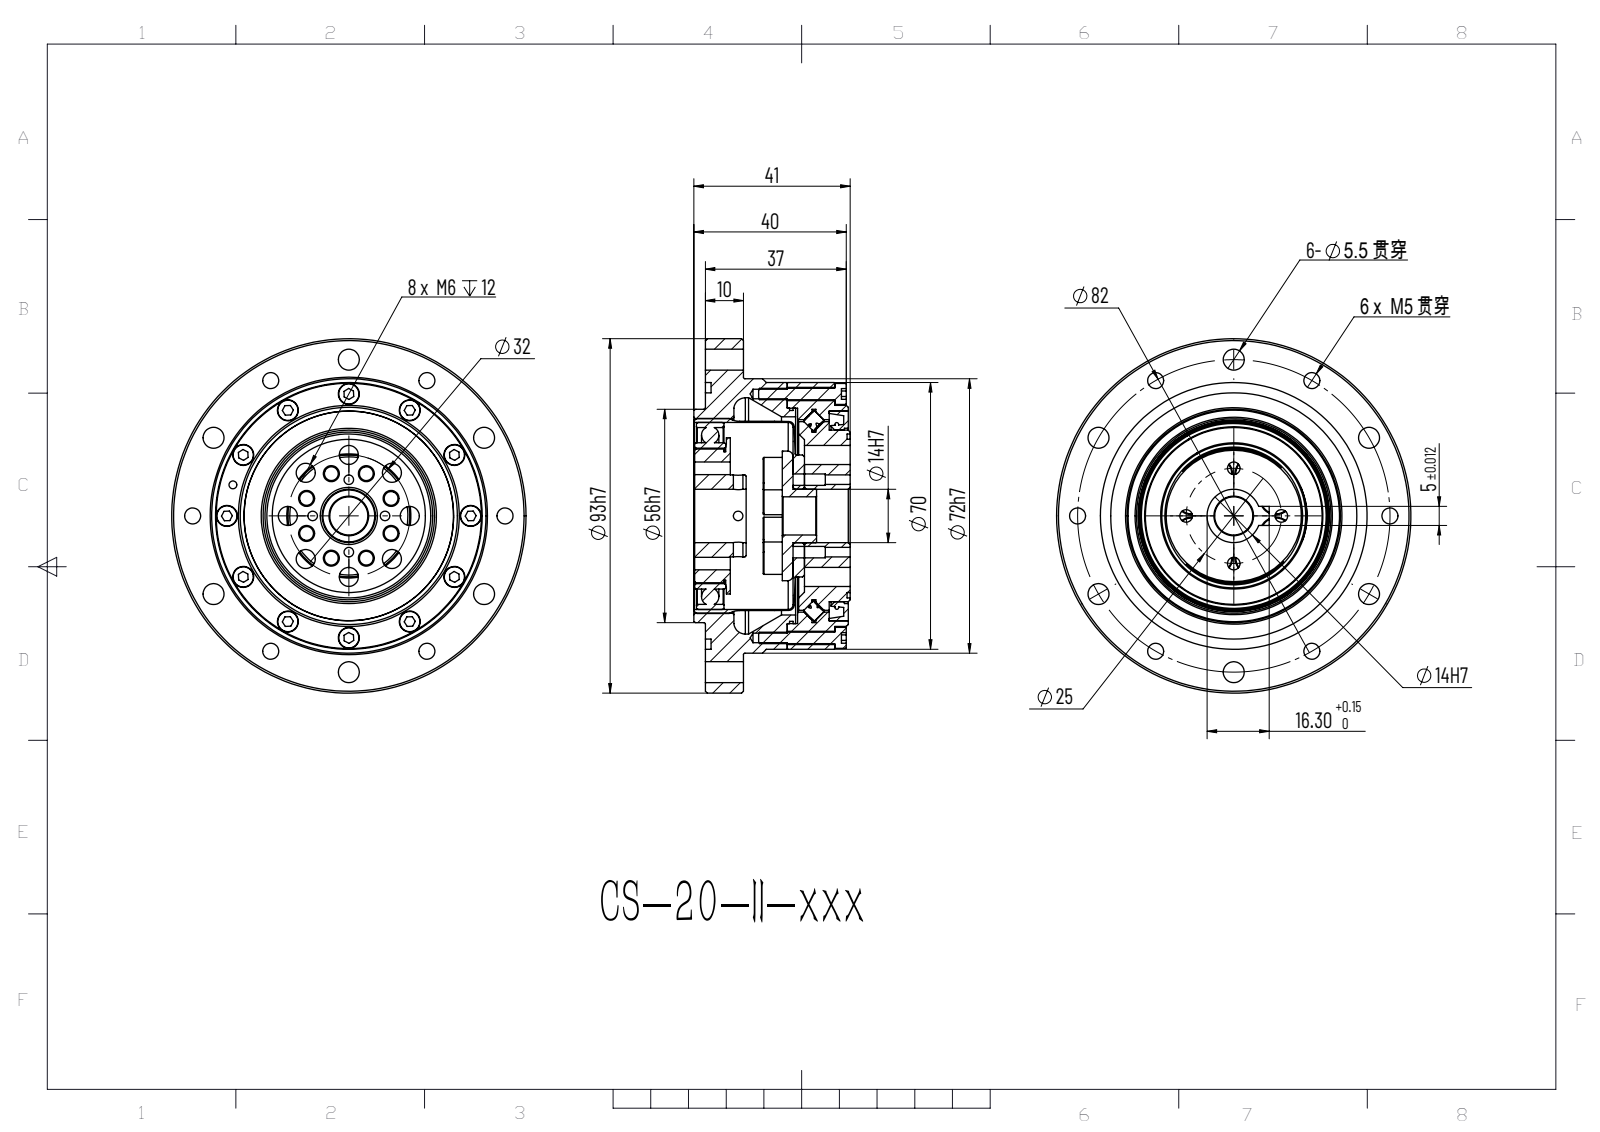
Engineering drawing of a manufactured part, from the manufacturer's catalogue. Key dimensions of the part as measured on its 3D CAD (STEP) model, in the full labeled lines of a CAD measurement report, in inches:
Part name (STEP PRODUCT): CS-20-II; hexagon socket head cap screws gb_GB_FASTENER_SCREWS_HSHCS M3X20-C; 3x10??; 20-?????? (+8 more)
STEP written by: ONSHAPE BY PTC INC, 1.201 (AP242_MANAGED_MODEL_BASED_3D_ENGINEERING_MIM_LF)
Units: inches
Bodies: 84 solids, 967 faces (487 planar, 234 cylindrical, 246 other)
Overall size (bounding box): 3.661 × 3.661 × 1.614
Volume: 7.696 in³ · Surface area: 130.7 in²
Round holes (diameter × count): ⌀0.098 ×16, ⌀0.165 ×14, ⌀0.217 ×14, ⌀0.138 ×12, ⌀0.197 ×9, ⌀0.118 ×4, ⌀0.13 ×4, ⌀0.081 ×1, ⌀0.114 ×1, ⌀0.394 ×1, ⌀0.551 ×1, ⌀1.4 ×1
Round bosses / shafts (diameter × count): ⌀0.118 ×62, ⌀0.217 ×12, ⌀0.335 ×8, ⌀0.197 ×8, ⌀3.661 ×1, ⌀2.835 ×1, ⌀2.756 ×1, ⌀2.543 ×1
Main face-to-face distances: 0.059, 0.453, 0.846, 0.512, 0.906, 0.394, 0.63, 0.433, 0.118, 0.543
Hole centre spacings: 1.614, 2.796, 3.119, 0.819, 2.048, 2.495, 2.778, 0.191
